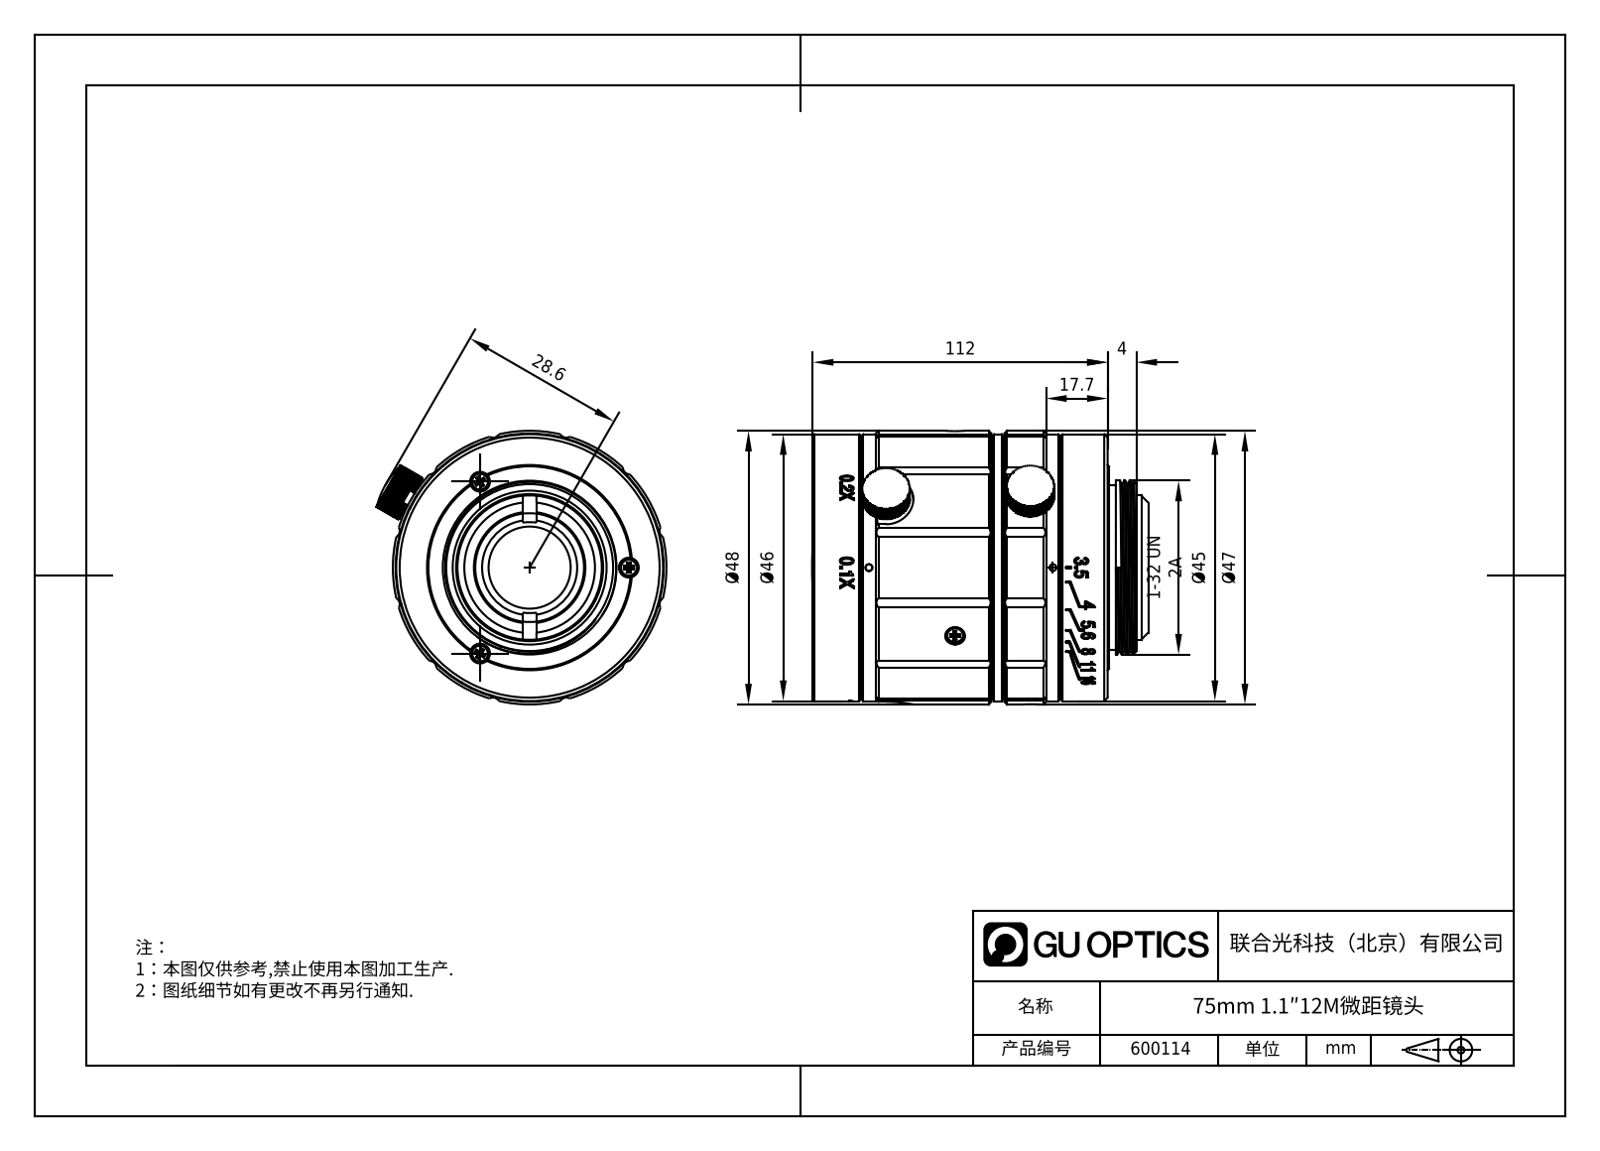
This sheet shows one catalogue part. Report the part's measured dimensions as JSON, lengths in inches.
{"part_name": "600114", "step_written_by": "SolidWorks 2020 (CONFIG_CONTROL_DESIGN)", "units": "inches", "bodies": {"solids": 20, "faces": 1771, "planar": 729, "cylindrical": 520, "other": 522}, "overall_size": [1.935, 1.668, 1.575], "volume_in3": 2.423, "surface_area_in2": 55.64, "round_holes": [[0.059, 6], [0.079, 6], [0.106, 6], [0.039, 4], [0.386, 1], [0.472, 1], [0.528, 1], [0.535, 1], [0.567, 1], [0.626, 1], [0.646, 1], [0.665, 1]], "round_bosses_or_shafts": [[0.098, 8], [0.055, 6], [0.081, 2], [1.575, 1], [1.535, 1], [1.48, 1], [1.472, 1], [1.461, 1]], "partial_cylinders_radius": [[0.039, 13], [0.004, 10], [0.157, 3], [0.134, 2], [0.138, 2], [0.483, 1], [0.591, 1], [0.766, 1]], "face_to_face_distances": [1.516, 1.461, 0.079, 1.437, 0.118, 0.772, 0.689, 1.319, 1.398, 0.063], "hole_center_spacings": [0.398, 0.433, 0.571, 0.831, 0.989]}
